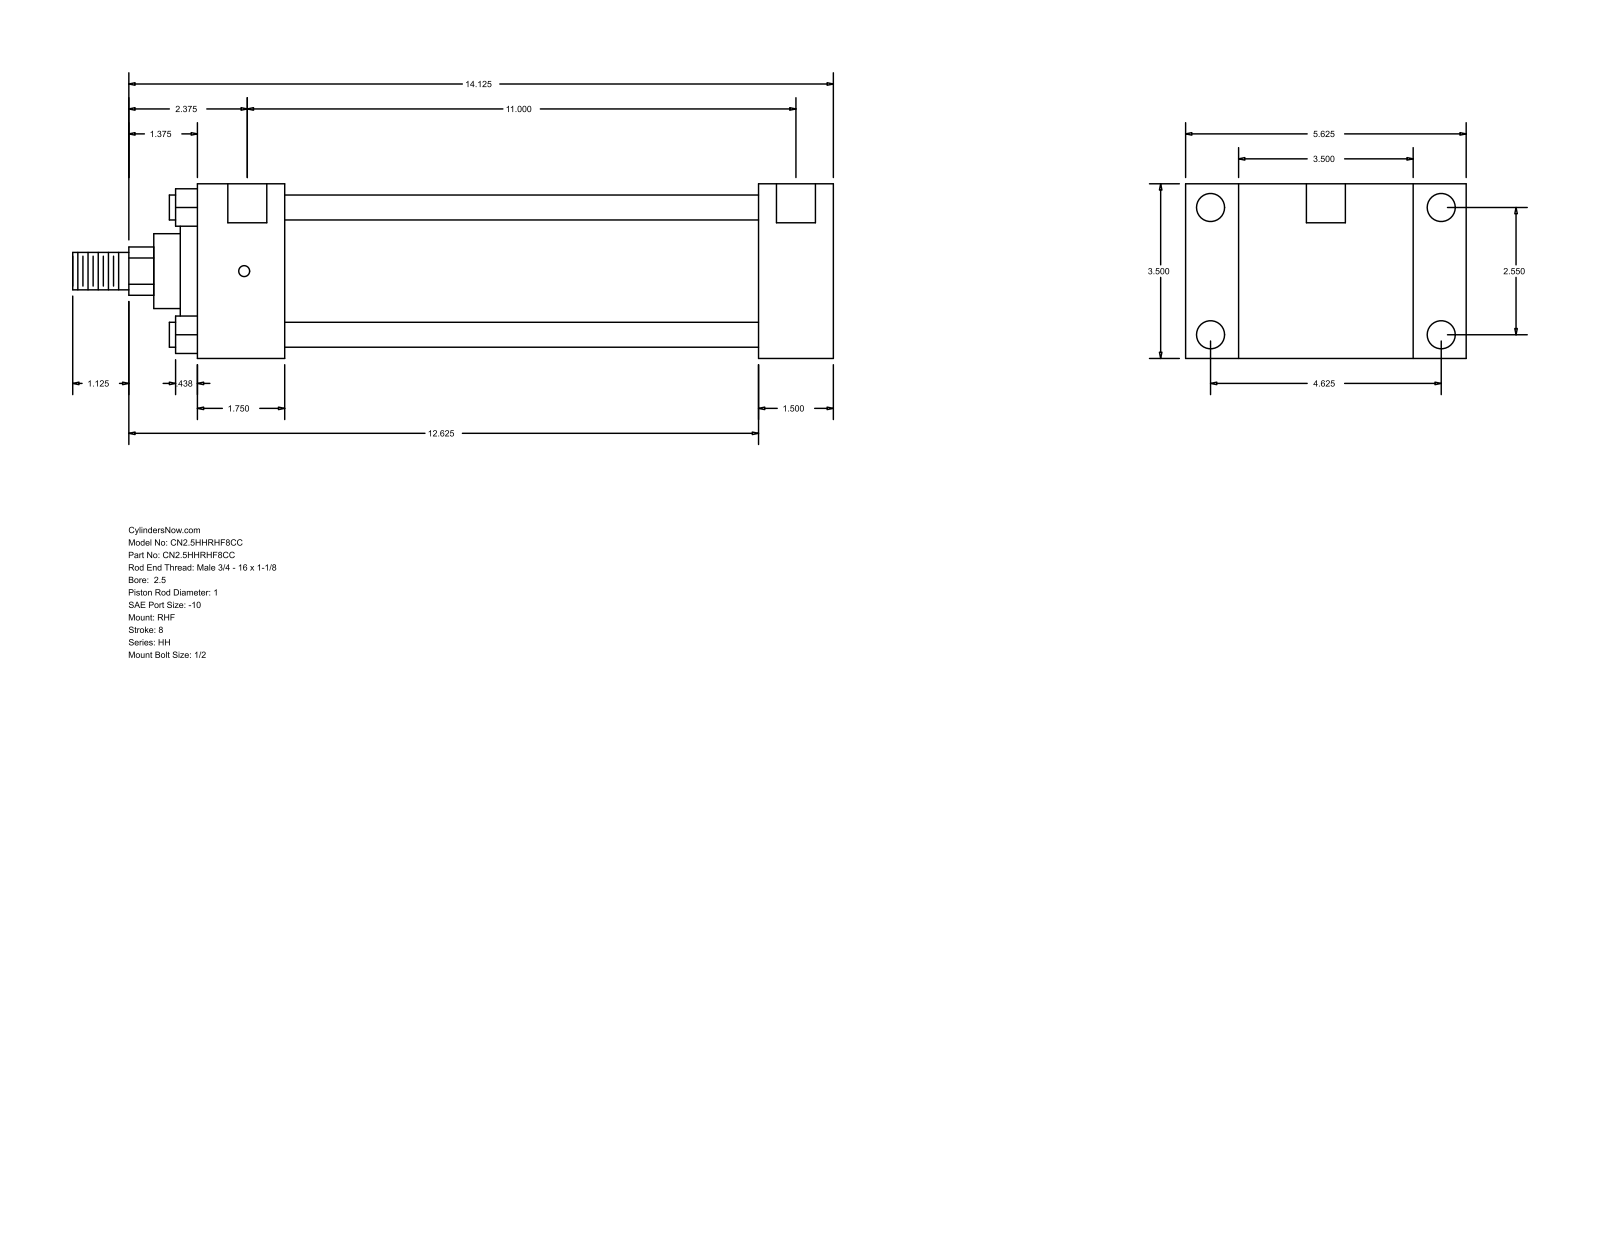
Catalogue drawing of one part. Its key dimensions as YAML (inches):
part_name: "HH_RHF__0250_1"
step_written_by: "GSSL Pune (CONFIG_CONTROL_DESIGN)"
units: inches
bodies: {solids: 0, faces: 90, planar: 61, cylindrical: 29, other: 0}
overall_size: [15.25, 5.625, 3.5]
round_holes:
  - {diameter: 0.219, count: 4}
  - {diameter: 0.563, count: 4}
  - {diameter: 0.781, count: 2}
round_bosses_or_shafts:
  - {diameter: 0.5, count: 4}
  - {diameter: 2.875, count: 1}
  - {diameter: 2.375, count: 1}
  - {diameter: 1.5, count: 1}
  - {diameter: 1, count: 1}
  - {diameter: 0.75, count: 1}
partial_cylinders:
  - {radius: 0.484, count: 1}
face_to_face_distances: [3.5, 1.5, 1.063, 4.563, 11.25, 12.75, 5.625, 1.75, 9.5, 11]
hole_center_spacings: [2.55, 4.625, 5.281, 11.125, 0.062, 0.063, 11, 11.062]
